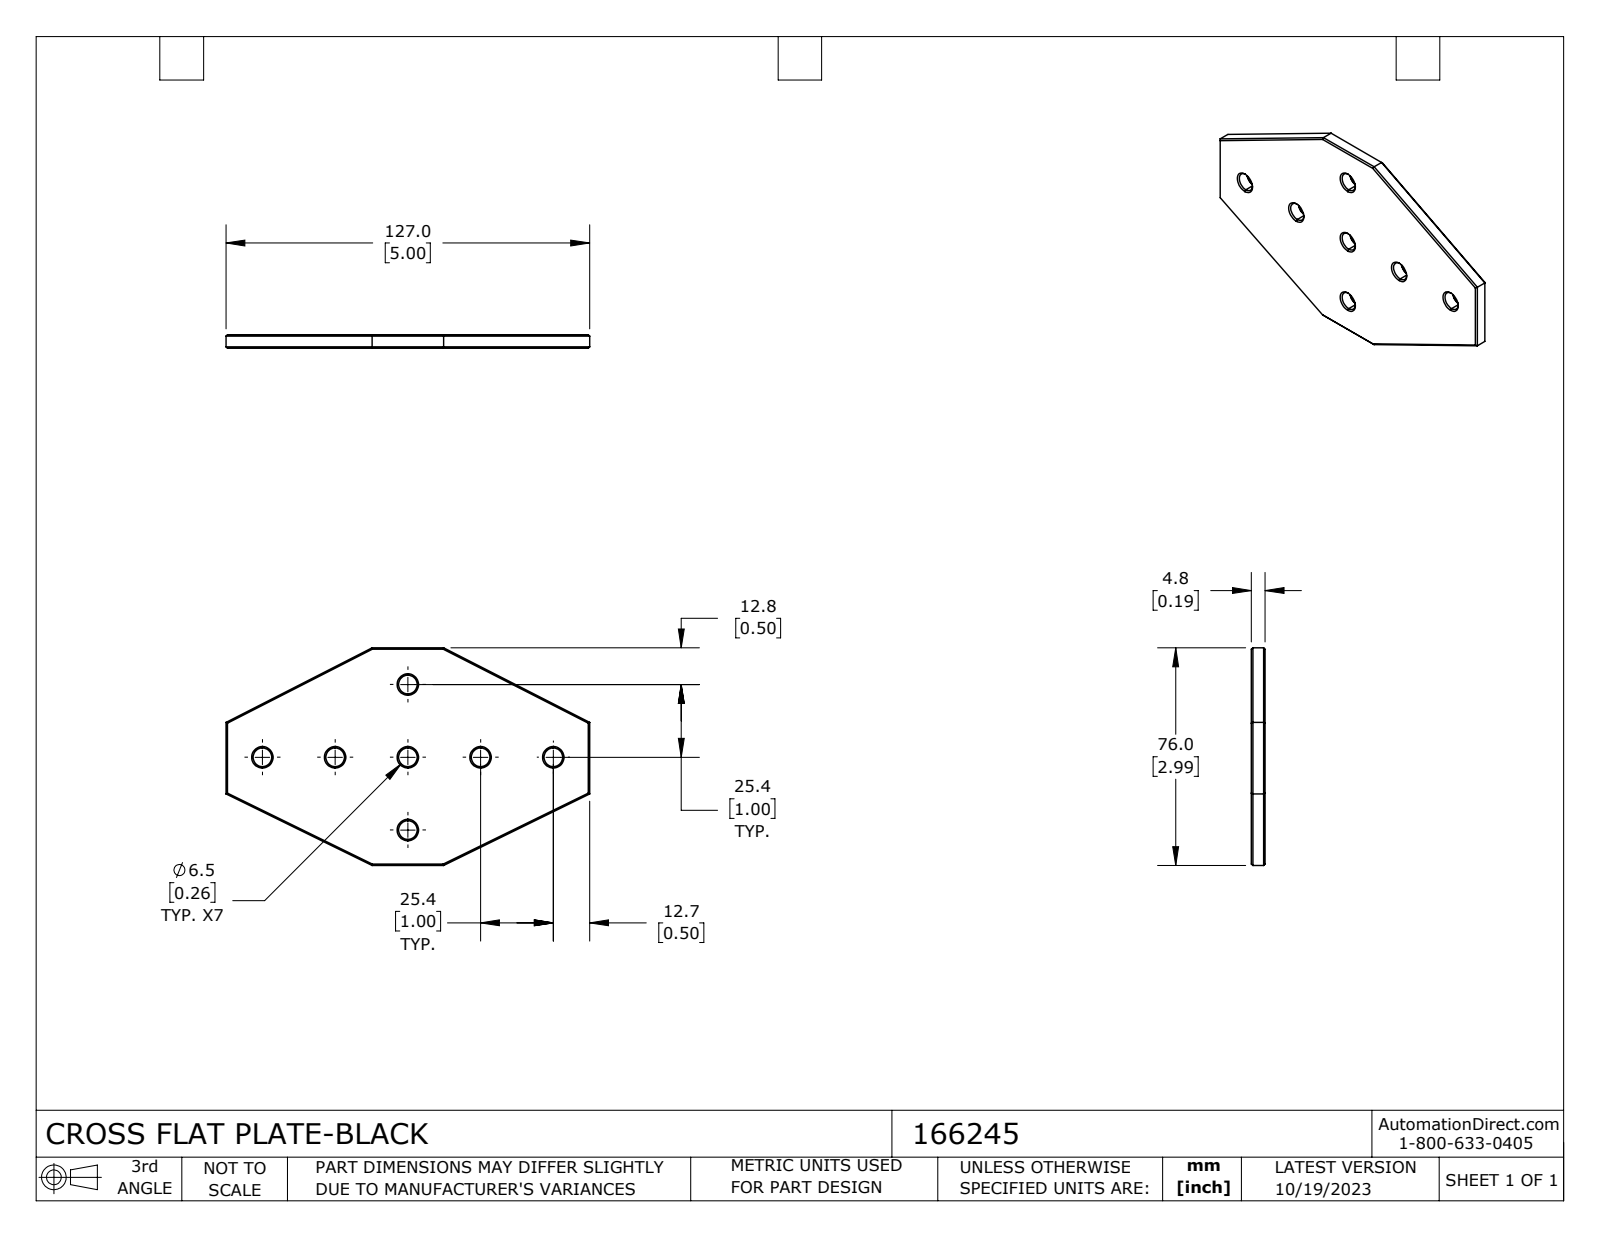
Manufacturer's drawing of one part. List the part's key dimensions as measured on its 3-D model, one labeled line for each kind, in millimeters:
Part name (STEP PRODUCT): 166245
STEP written by: SolidWorks 2023 (CONFIG_CONTROL_DESIGN)
Units: millimetres
Bodies: 1 solid, 68 faces (26 planar, 14 cylindrical, 28 other)
Overall size (bounding box): 127 × 76 × 4.76
Volume: 32 355 mm³ · Surface area: 15 609 mm²
Round holes (diameter × count): ⌀6.5 ×7
Main face-to-face distances: 4.76, 127, 76, 56.39, 92.45
Hole centre spacings: 25.4, 35.92, 50.8, 56.8, 76.2, 101.6
